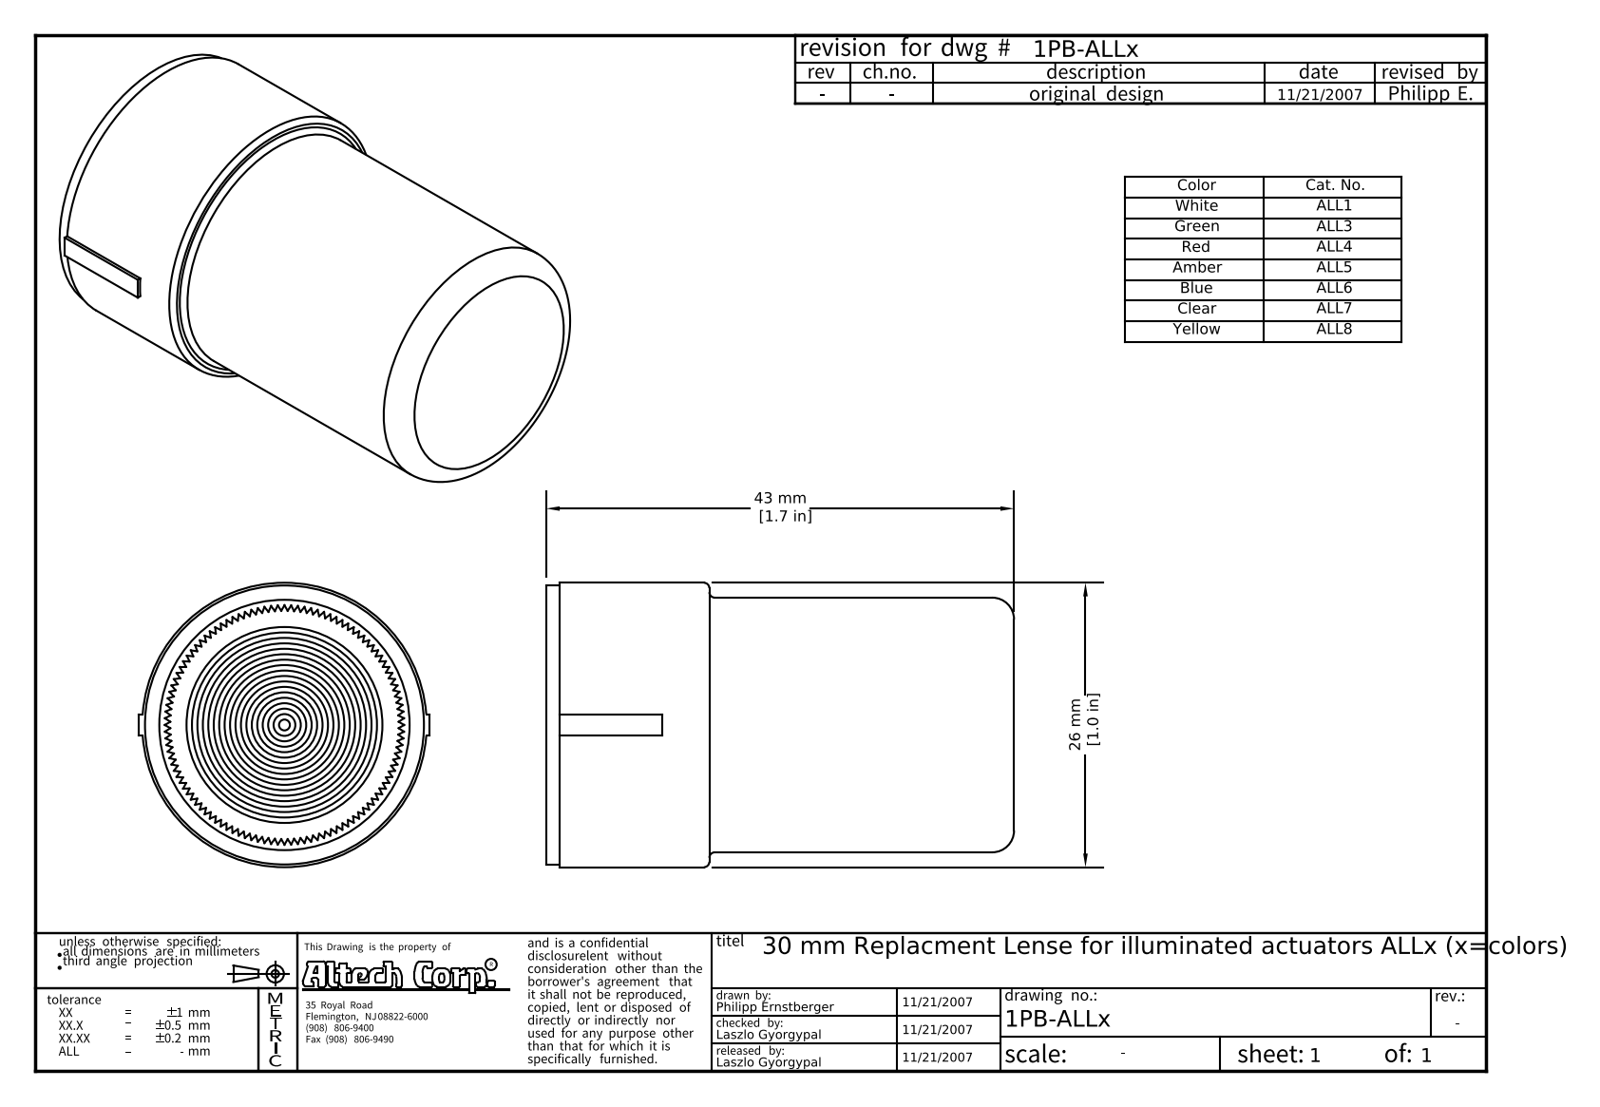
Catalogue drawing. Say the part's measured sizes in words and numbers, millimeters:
The part is named "ALLx". Its 3-D file was written by "Autodesk Inventor 2008 (AUTOMOTIVE_DESIGN)". It is 1 solid with 375 faces: 238 planar, 116 cylindrical and 21 other. Overall it measures 43 by 26.75 by 26.14 millimeters. Its volume is 4 808 cubic millimeters and its surface area 9 452 square millimeters. Round holes: 1 of diameter 23. Round bosses or shafts: 1 of diameter 26.14, 1 of diameter 25.63, 1 of diameter 23.4. Partial cylindrical surfaces (rounded edges, fillets, slot ends): 1 of radius 10.5. The main face-to-face distances are 11, 11.01, 10.99, 2, 41, 43, 5.25, 35.75, 37.75, 15.
